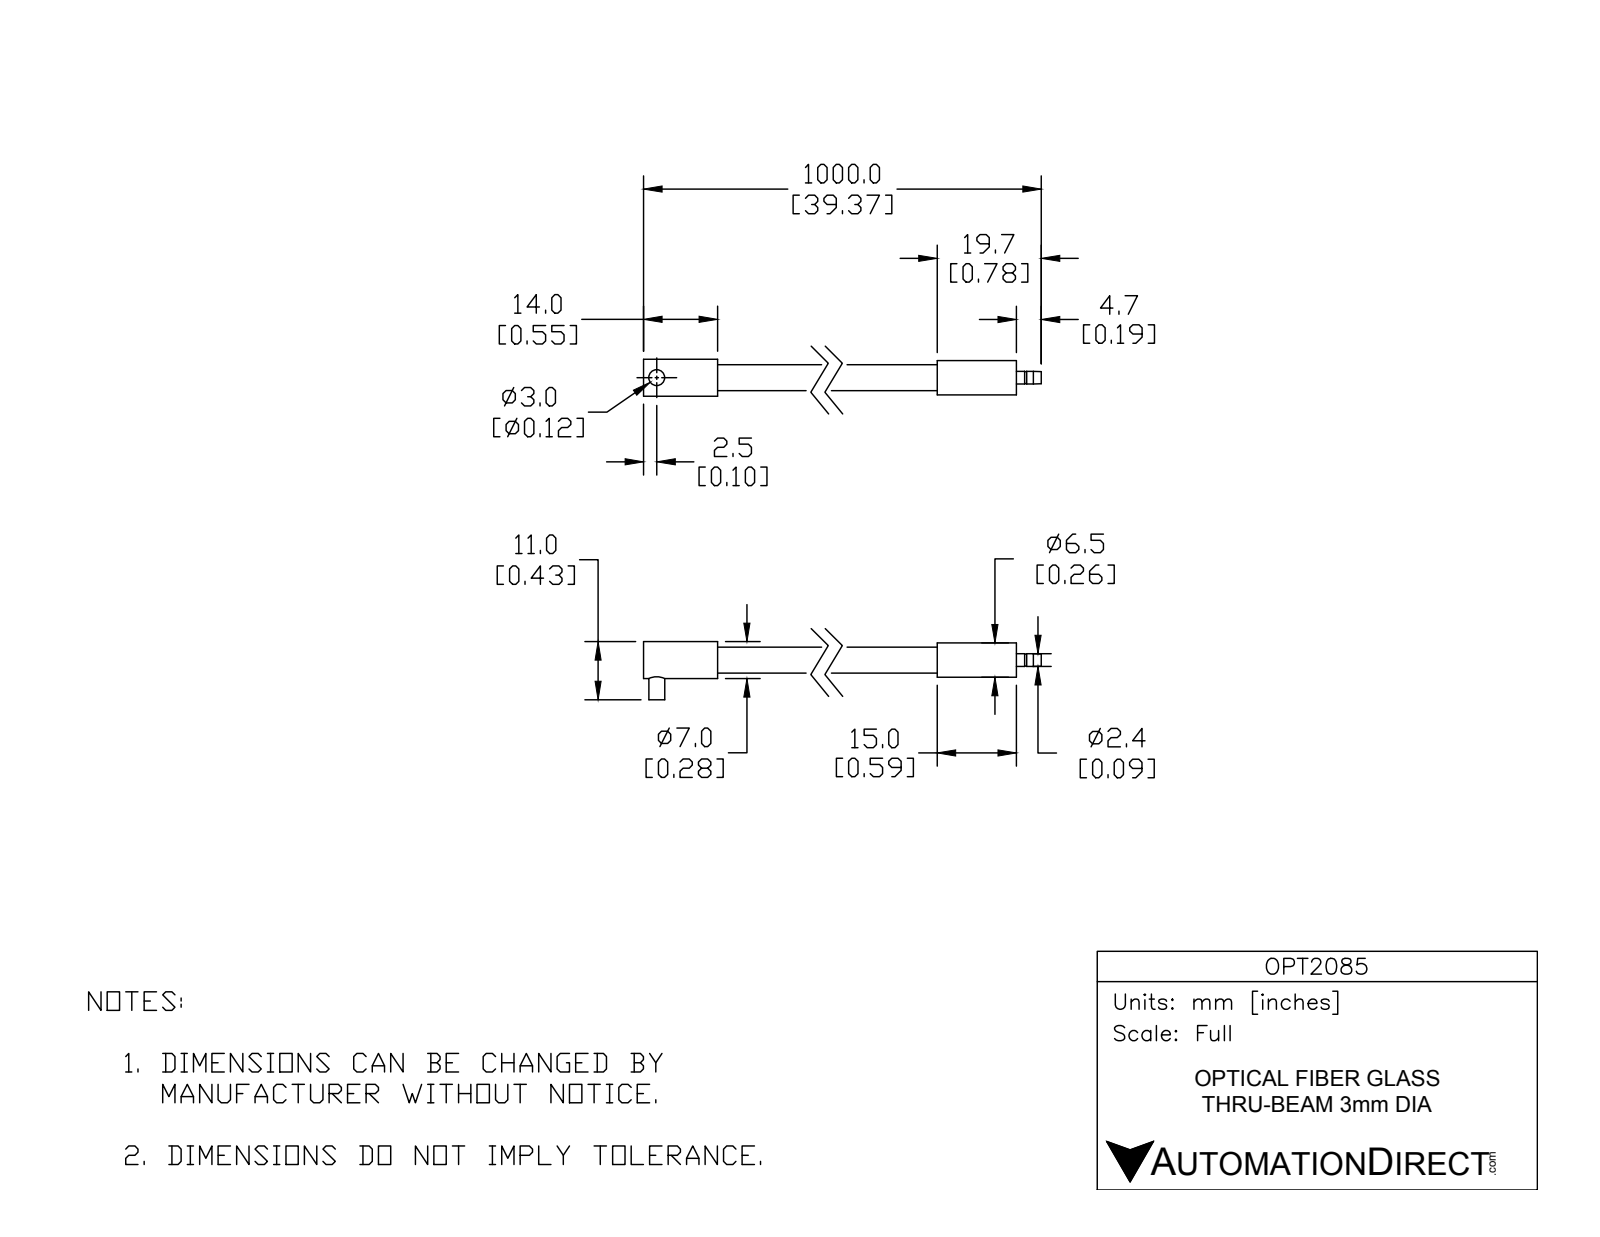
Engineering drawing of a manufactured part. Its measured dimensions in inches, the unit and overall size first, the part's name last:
Units: inches
Overall size (bounding box): 39.37 × 0.433 × 0.276
Round bosses / shafts (diameter × count): ⌀0.276 ×1, ⌀0.256 ×1, ⌀0.193 ×1, ⌀0.118 ×1, ⌀0.094 ×1
Main face-to-face distances: 39.185, 0.551, 38.634, 38.594, 38.043, 0.591, 39.37, 38.819, 0.776, 0.185
Volume: 1.178 in³ · Surface area: 24.29 in²
Bodies: 1 solid, 24 faces (6 planar, 12 cylindrical, 6 other)
Part name (STEP PRODUCT): OPT2085
STEP written by: SolidWorks 2014 (AUTOMOTIVE_DESIGN)
